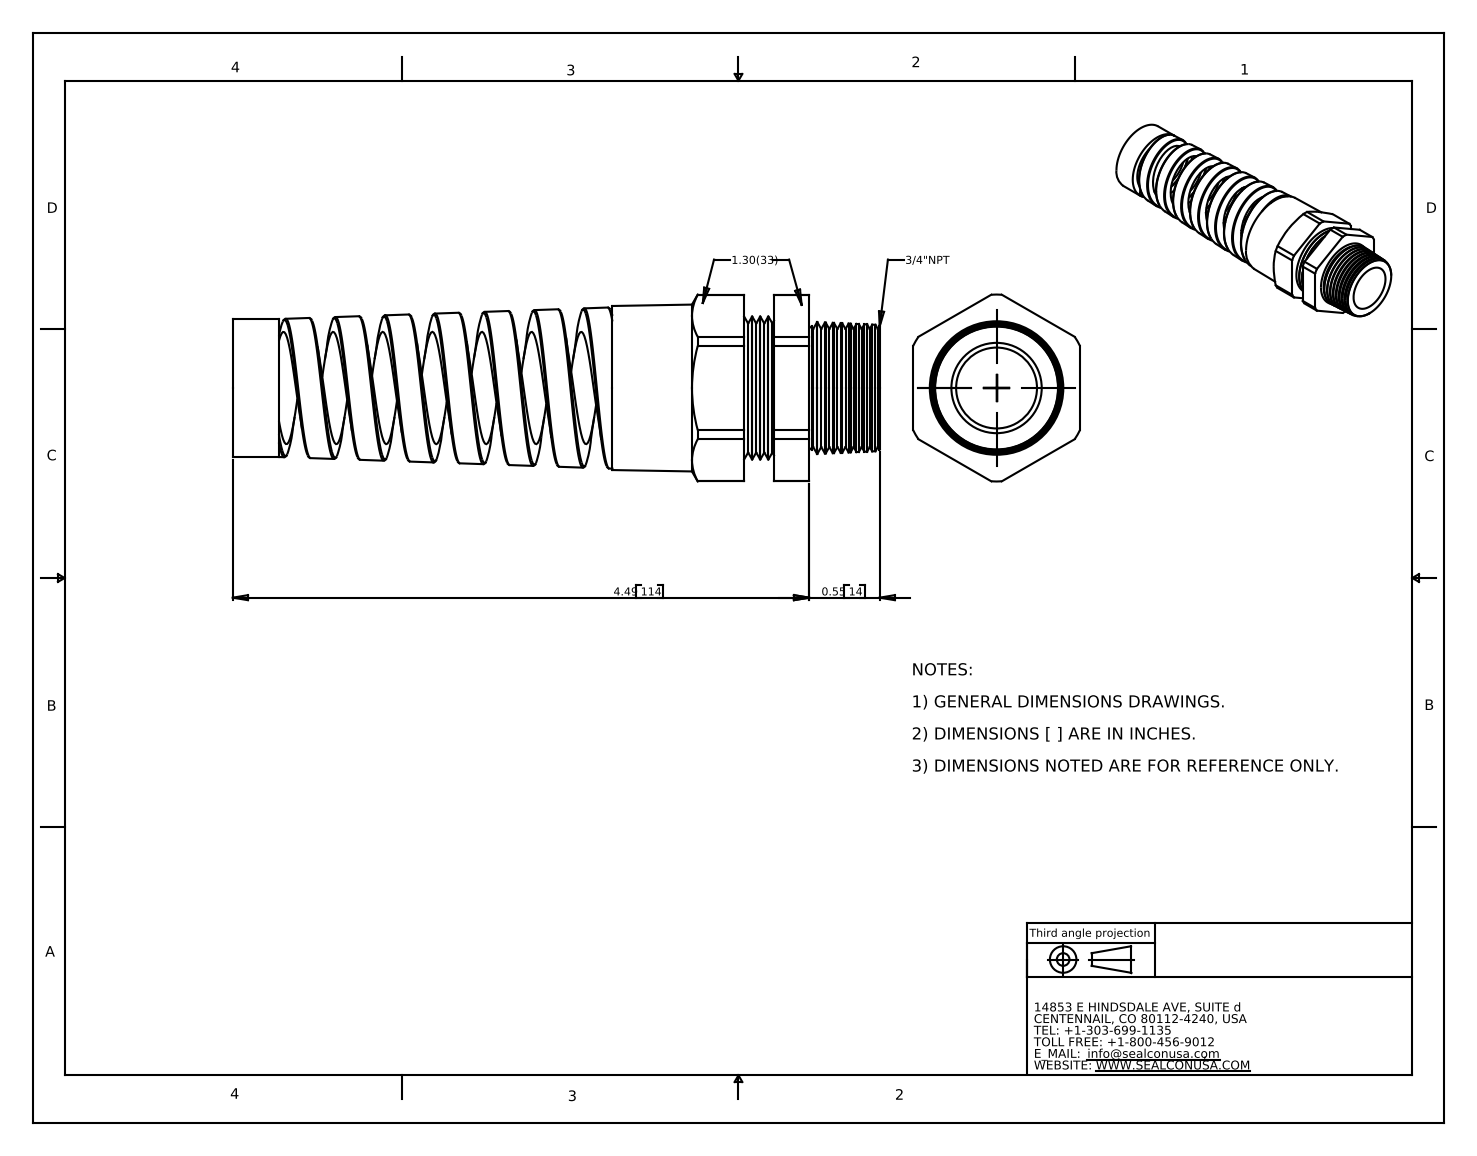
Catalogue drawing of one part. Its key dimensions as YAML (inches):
part_name: "CF21NR-BK"
step_written_by: "SolidWorks 2007 (CONFIG_CONTROL_DESIGN)"
units: inches
bodies: {solids: 1, faces: 163, planar: 19, cylindrical: 39, other: 105}
overall_size: [5.04, 1.456, 1.3]
volume: 2.479
surface_area: 35.15
round_holes:
  - {diameter: 0.63, count: 1}
  - {diameter: 0.875, count: 1}
round_bosses_or_shafts:
  - {diameter: 1.113, count: 1}
  - {diameter: 1.075, count: 1}
partial_cylinders:
  - {radius: 0.728, count: 1}
face_to_face_distances: [1.3, 1.532, 1.026, 0.506, 1.259, 0.232, 0.274, 2.082, 1.056, 0.824]
